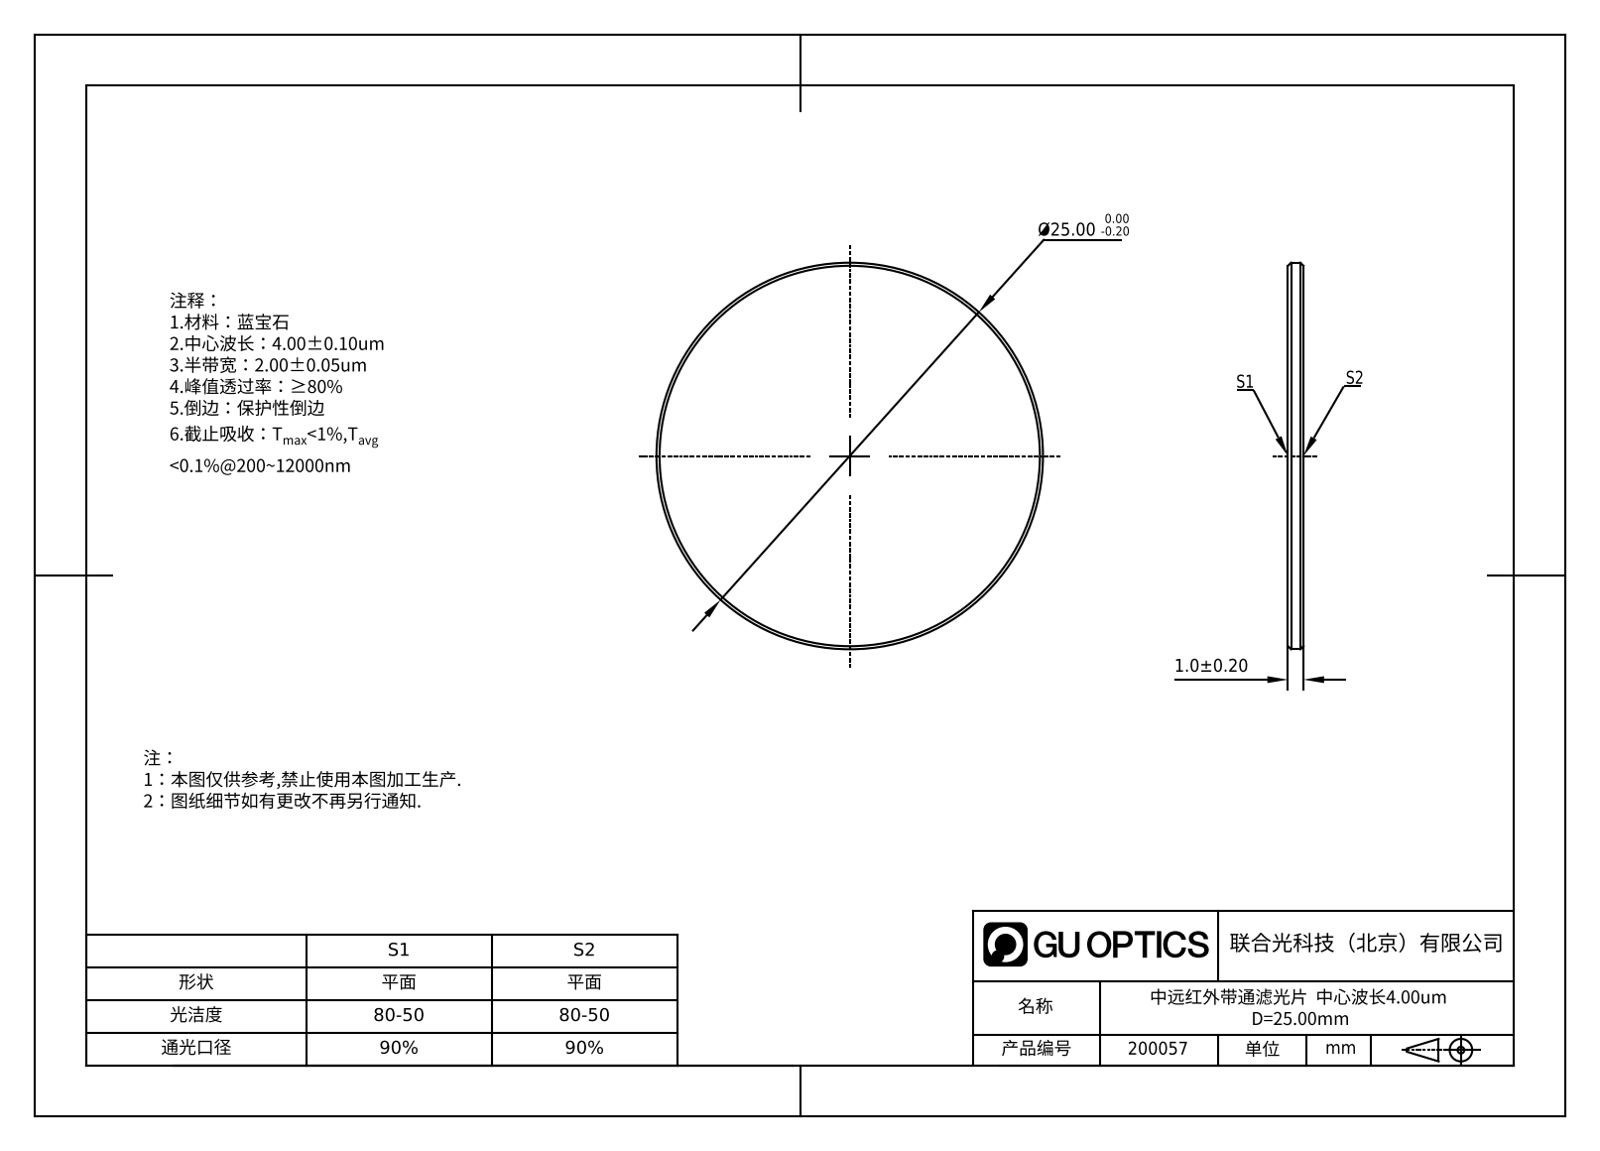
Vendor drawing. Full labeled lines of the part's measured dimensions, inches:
Part name (STEP PRODUCT): GNIF-2000-4000-D25
STEP written by: SolidWorks 2022 (AUTOMOTIVE_DESIGN)
Units: inches
Bodies: 1 solid, 8 faces (2 planar, 2 cylindrical, 4 other)
Overall size (bounding box): 0.984 × 0.984 × 0.039
Volume: 0.03 in³ · Surface area: 1.615 in²
Round bosses / shafts (diameter × count): ⌀0.984 ×1
Main face-to-face distances: 0.039
